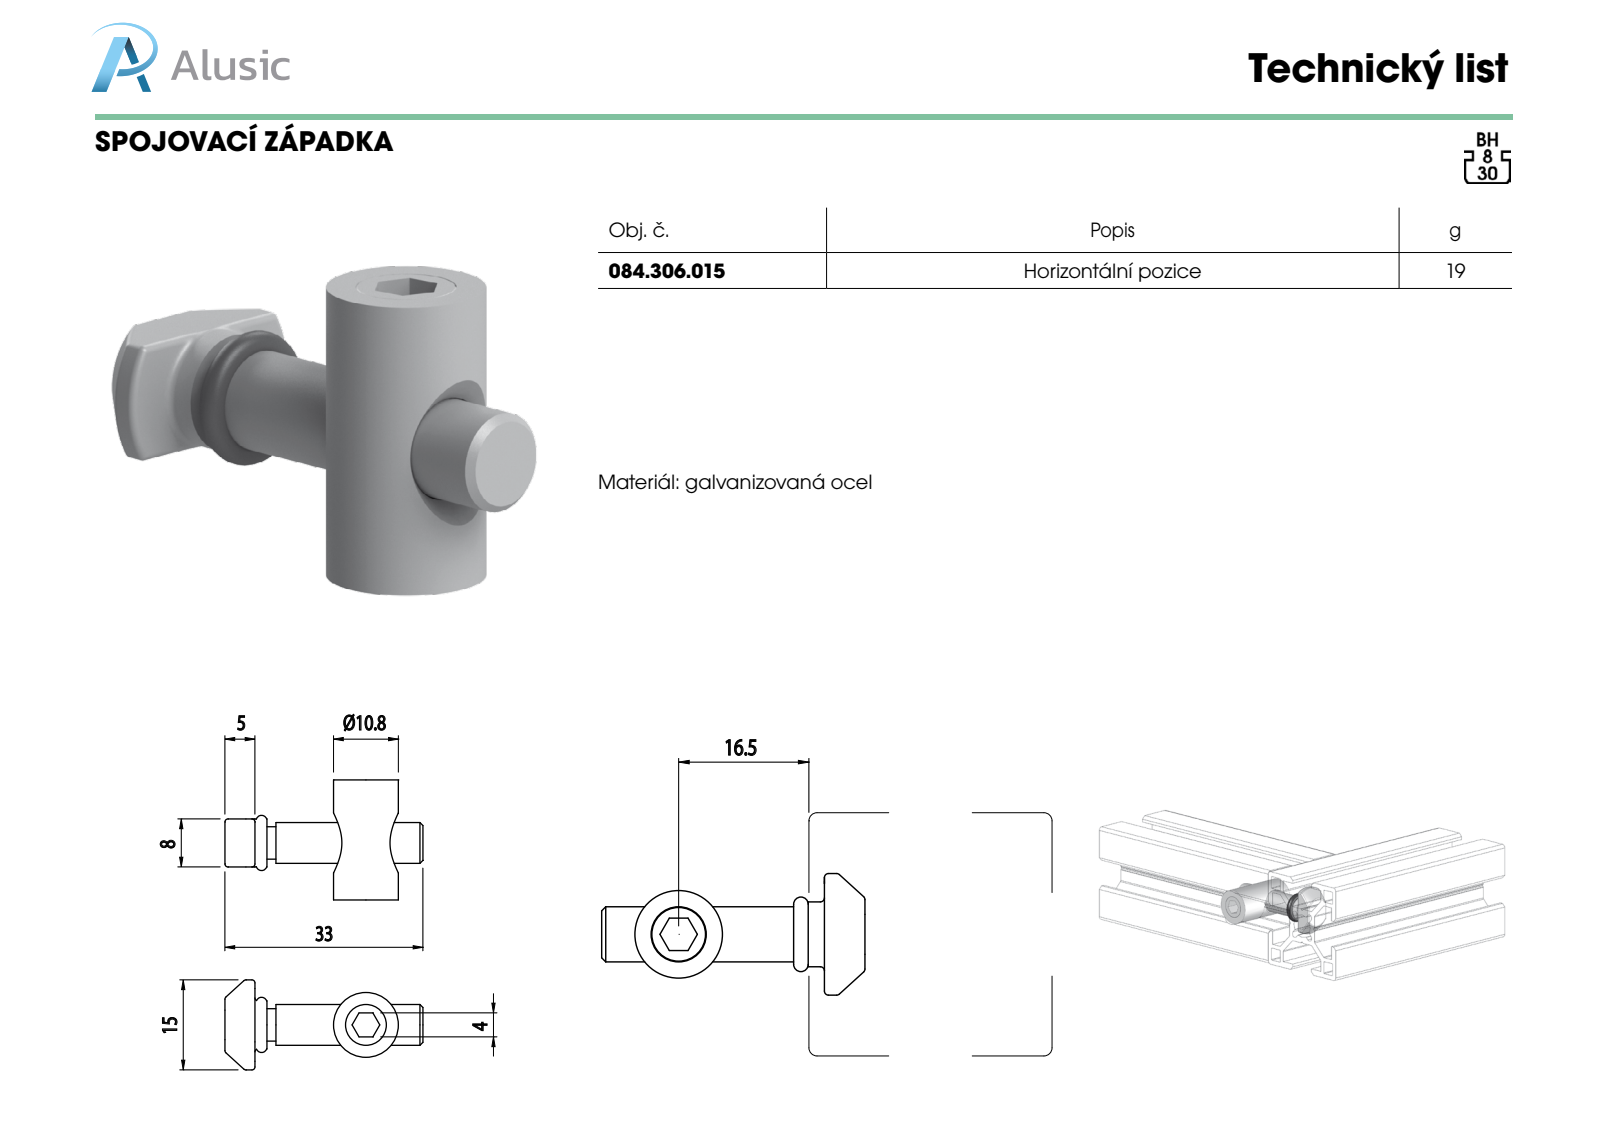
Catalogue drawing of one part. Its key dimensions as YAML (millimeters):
part_name: "084.306.015; O-rings series A_ALUSIC_O-ring 5.6x1.8-A-ISO 3601-1; 3.JNT.004A; Socket Set Screw Cone Point_ALUSIC_PreviewCfg (+1 more)"
step_written_by: "SolidWorks 2012 (CONFIG_CONTROL_DESIGN)"
units: millimeters
bodies: {solids: 4, faces: 146, planar: 18, cylindrical: 40, other: 88}
overall_size: [33, 20, 15]
volume: 2874
surface_area: 2739
round_holes:
  - {diameter: 6.8, count: 1}
  - {diameter: 7, count: 1}
round_bosses_or_shafts:
  - {diameter: 8, count: 2}
  - {diameter: 10.8, count: 1}
  - {diameter: 6.8, count: 1}
  - {diameter: 5.4, count: 1}
partial_cylinders:
  - {radius: 0.5, count: 8}
  - {radius: 7.5, count: 1}
face_to_face_distances: [20, 5, 5.5, 14.5, 13.5, 8, 6.5, 4, 7, 2]
